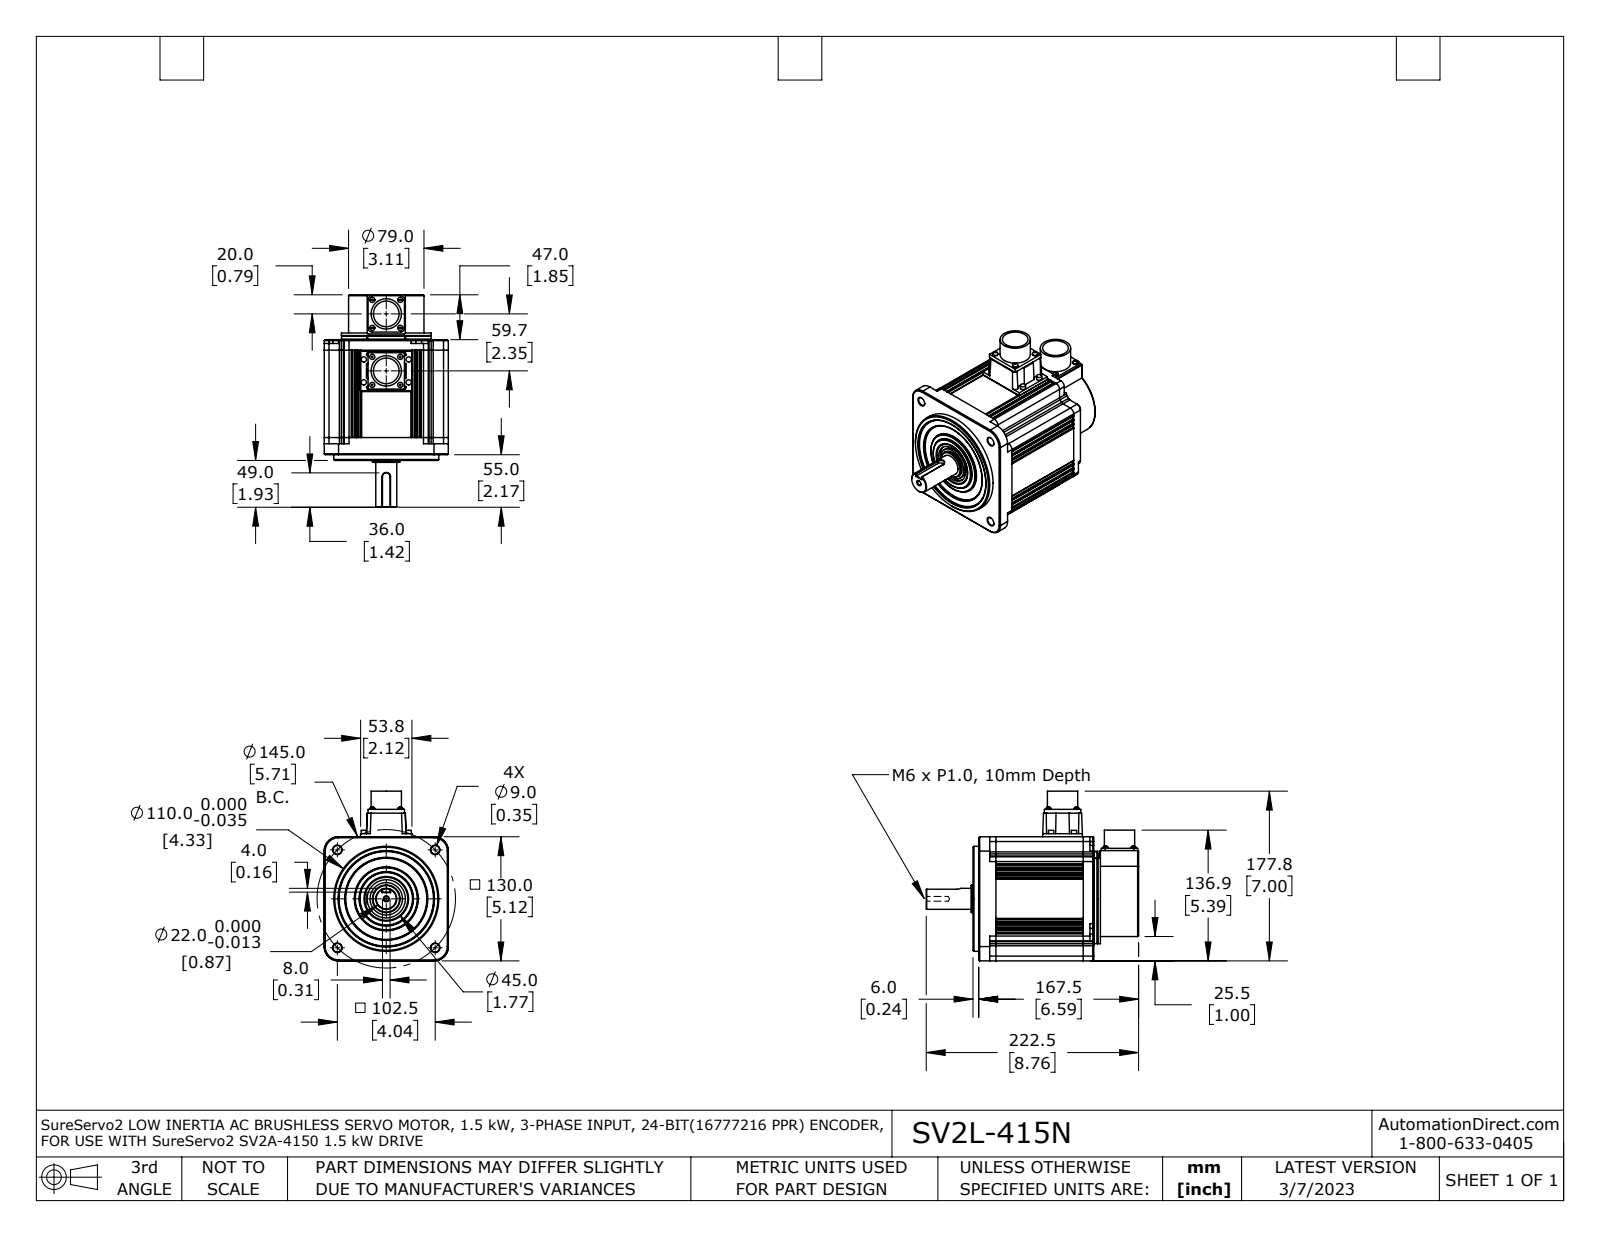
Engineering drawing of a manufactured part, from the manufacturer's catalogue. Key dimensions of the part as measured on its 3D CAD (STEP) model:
Part name (STEP PRODUCT): SV2M-x15N fxt
STEP written by: SolidWorks 2021 (AUTOMOTIVE_DESIGN)
Units: inches
Bodies: 2 solids, 627 faces (286 planar, 182 cylindrical, 159 other)
Overall size (bounding box): 8.76 × 6.998 × 5.118
Volume: 134 in³ · Surface area: 226.8 in²
Round holes (diameter × count): ⌀0.354 ×4, ⌀1.058 ×2, ⌀0.197 ×1, ⌀1.142 ×1, ⌀1.575 ×1, ⌀1.772 ×1, ⌀3.386 ×1, ⌀3.937 ×1
Round bosses / shafts (diameter × count): ⌀0.217 ×6, ⌀0.213 ×6, ⌀1.25 ×2, ⌀4.331 ×1, ⌀3.701 ×1, ⌀3.11 ×1, ⌀2.598 ×1, ⌀2.205 ×1
Partial cylindrical surfaces — rounded edges, fillets, slot ends (radius × count): R0.039 ×70, R0.02 ×10, R0.157 ×9, R0.118 ×8, R0.197 ×8
Main face-to-face distances: 4.291, 0.827, 5.118, 4.744, 1.85, 2.402, 6.594, 0.211, 0.959, 0.118
Hole centre spacings: 2.855, 4.037, 5.709, 2.35
